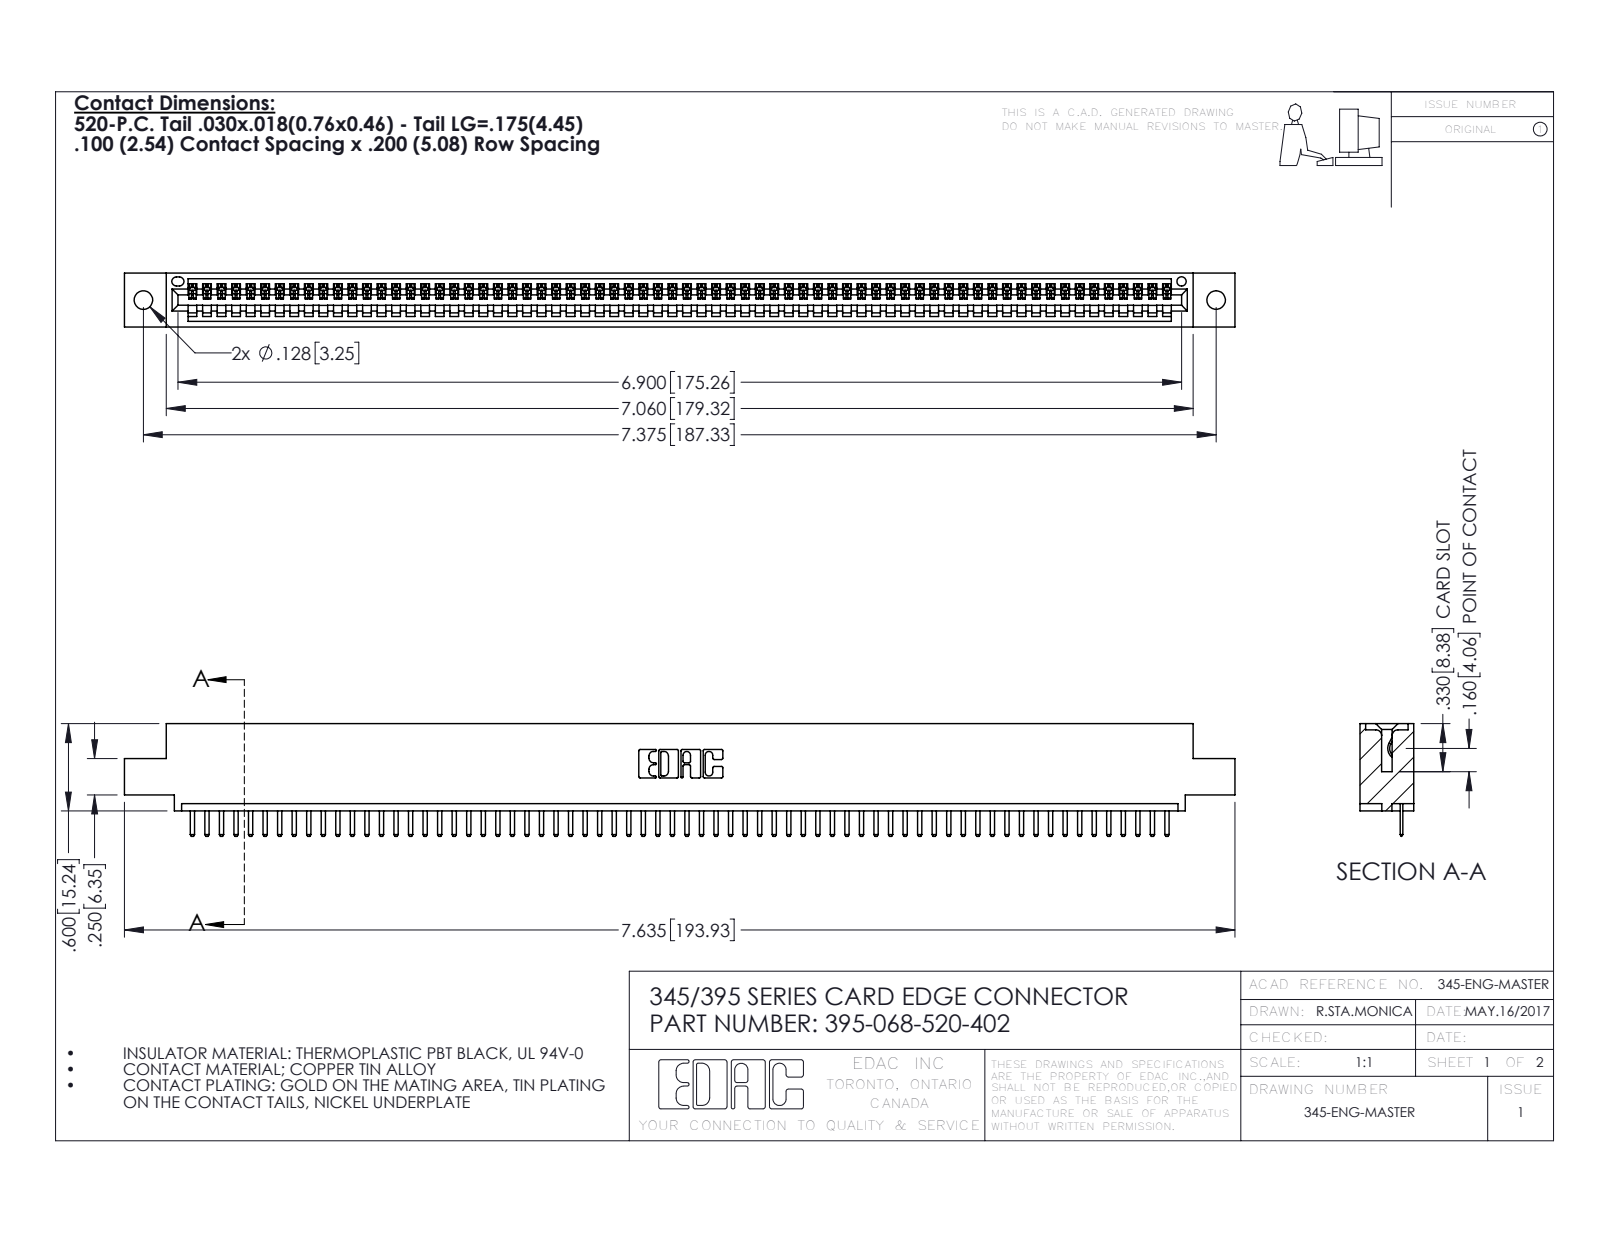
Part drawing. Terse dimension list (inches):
name: 395-068-520-402; 345 Part_0.110 Offset - 0.128 Dia; 345-292-001_345-293-120
written by: SolidWorks 2016 (CONFIG_CONTROL_DESIGN)
unit: in
bodies: 69 solids, 4346 faces (2940 planar, 1406 cylindrical, 0 other)
size: 7.635 × 0.775 × 0.37
volume: 1.118 in³; area: 37.01 in²
holes: 2× ⌀0.128, 1× ⌀0.064
rounds: 138× R0.01, 136× R0.006, 22× R0.01, 6× R0.007, 6× R0.031, 3× R0.026, 2× R0.031, 2× R0.04
face distances: 0.298, 0.072, 0.37, 0.2, 0.098, 0.272, 0.025, 0.225, 0.072, 0.149
hole spacings: 0.27, 7.139, 7.375
